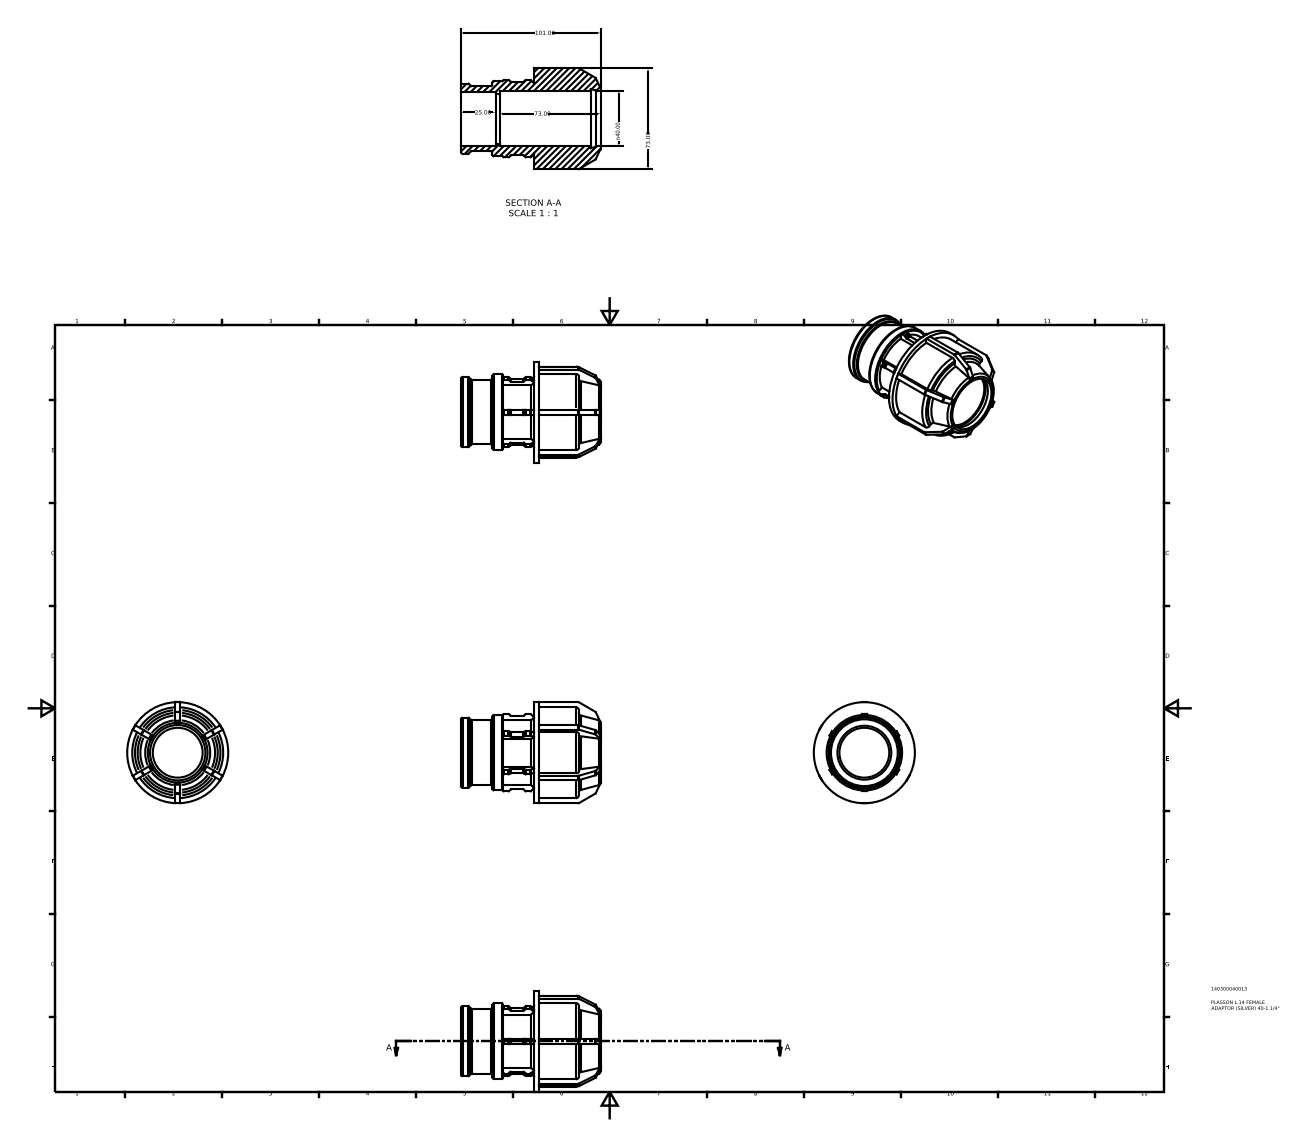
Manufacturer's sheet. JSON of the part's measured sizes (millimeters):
{"part_name": "140300040013", "step_written_by": "Autodesk Inventor 2015 (AUTOMOTIVE_DESIGN)", "units": "millimeters", "bodies": {"solids": 1, "faces": 261, "planar": 159, "cylindrical": 68, "other": 34}, "overall_size": [101, 73, 73], "volume_mm3": 122849, "surface_area_mm2": 40066, "round_holes": [[36, 1], [38.95, 1], [40, 1]], "round_bosses_or_shafts": [[73, 1], [65.7, 1], [54.53, 1], [50.64, 1], [46.74, 1]], "partial_cylinders_radius": [[1.2, 48]], "face_to_face_distances": [3.65, 3.64, 52.82, 56.47, 3.66, 73, 30.25, 22.57, 26.22, 2.25]}
